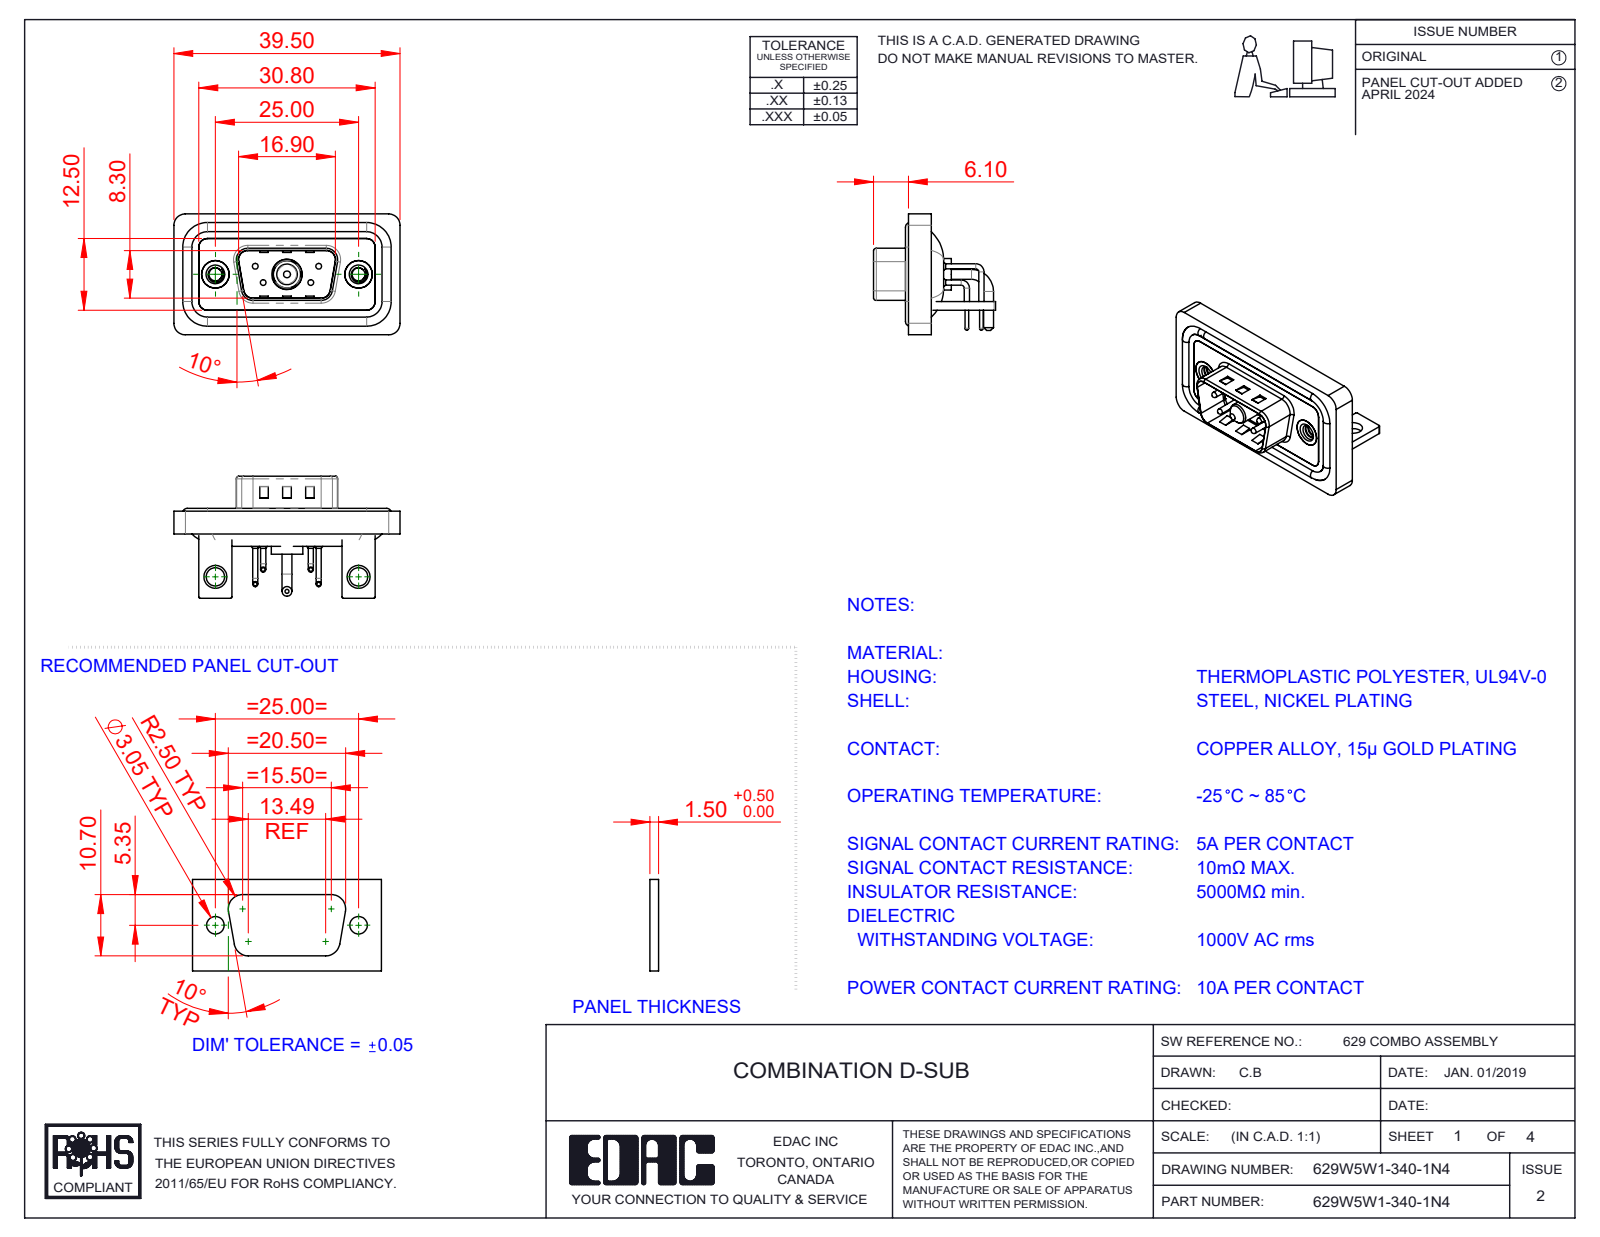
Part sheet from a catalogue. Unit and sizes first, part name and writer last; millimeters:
Units: millimetres
Overall size (bounding box): 39.5 × 21.3 × 21.1
Round holes (diameter × count): ⌀0.75 ×4, ⌀1.6 ×4, ⌀2 ×4, ⌀2.26 ×2, ⌀3.2 ×2, ⌀4 ×2, ⌀4.8 ×2, ⌀5 ×2, ⌀4.85 ×1, ⌀5.3 ×1
Round bosses / shafts (diameter × count): ⌀0.9 ×8, ⌀1.6 ×4, ⌀1.5 ×4, ⌀1 ×4, ⌀0.65 ×4, ⌀4.9 ×2, ⌀1.7 ×2, ⌀5.5 ×1
Partial cylindrical surfaces — rounded edges, fillets, slot ends (radius × count): R2 ×19, R1.5 ×18, R0.25 ×16, R0.5 ×9, R1.6 ×8, R0.6 ×4, R0.65 ×4, R0.9 ×4
Main face-to-face distances: 0.4, 1.5, 0.8, 2.9, 1.1, 2.1, 1.2, 1.6, 2.5, 3.7
Hole centre spacings: 3.16, 5.72, 7.1, 12.5, 18.1, 25, 4.39, 4.4
Volume: 4 696 mm³ · Surface area: 7 700 mm²
Bodies: 15 solids, 934 faces (431 planar, 363 cylindrical, 140 other)
Part name (STEP PRODUCT): 629Combo Waterproof Housing_09 Contacts; 629W5W1-340-1N4; 629Combo Shell Rear_09 Contacts; 629Combo Threaded Rivet_3 (+6 more)
STEP written by: SolidWorks 2023 (CONFIG_CONTROL_DESIGN)
